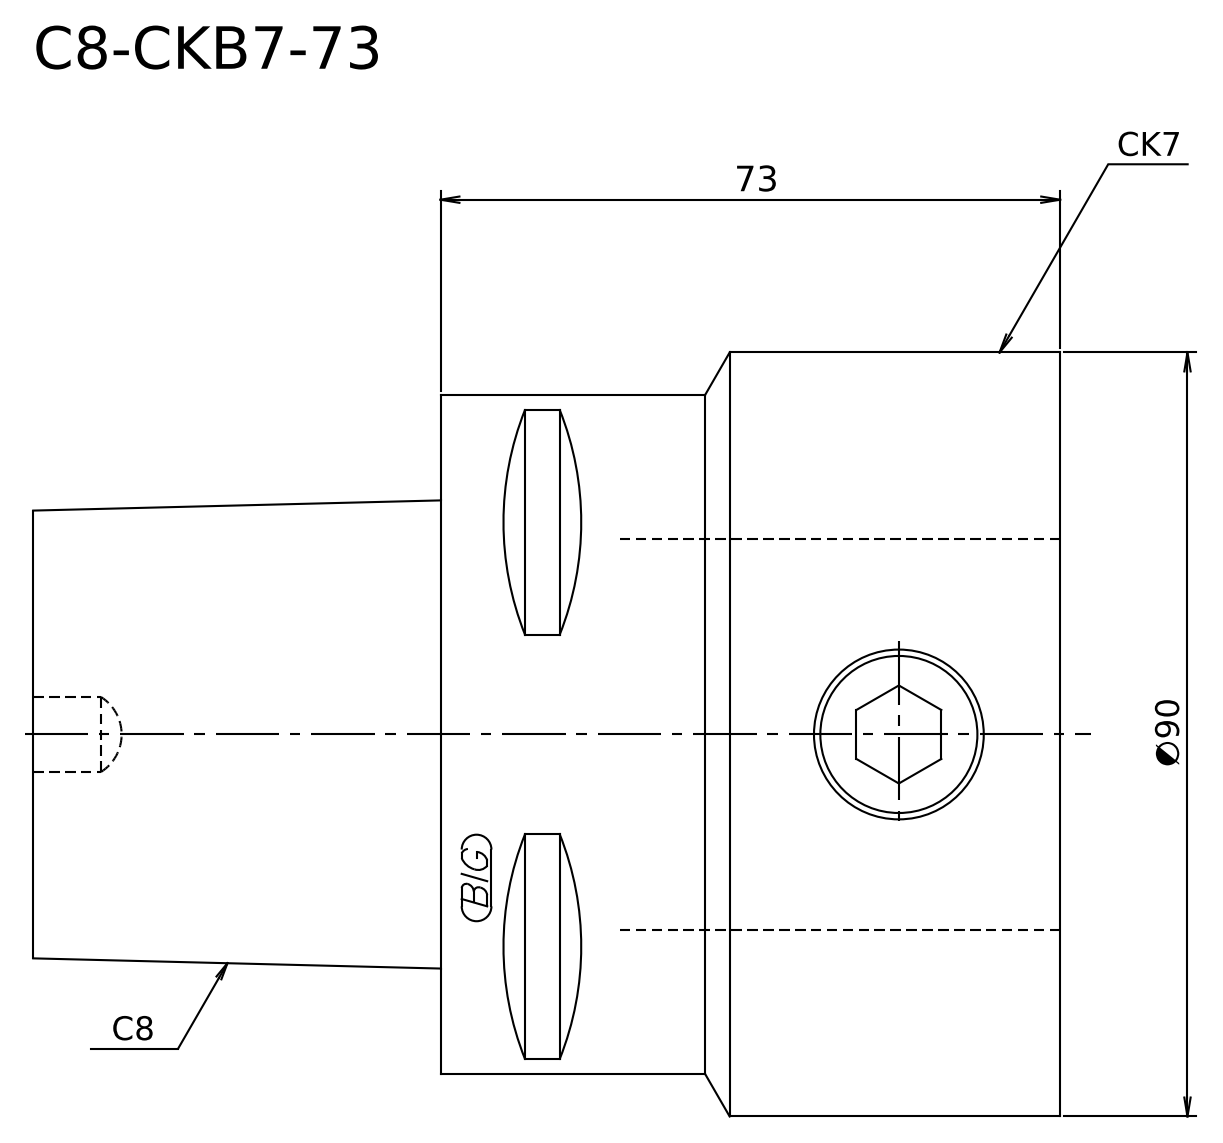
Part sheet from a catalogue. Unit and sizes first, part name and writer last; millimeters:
Units: millimetres
Overall size (bounding box): 121 × 90 × 90
Round bosses / shafts (diameter × count): ⌀90 ×1, ⌀79.98 ×1
Main face-to-face distances: 73, 121, 48
Volume: 527 000 mm³ · Surface area: 39 668 mm²
Bodies: 1 solid, 8 faces (3 planar, 2 cylindrical, 3 other)
STEP written by: Kubotek KeyCreator V8.5.1 (14335) (CONFIG_CONTROL_DESIGN)
